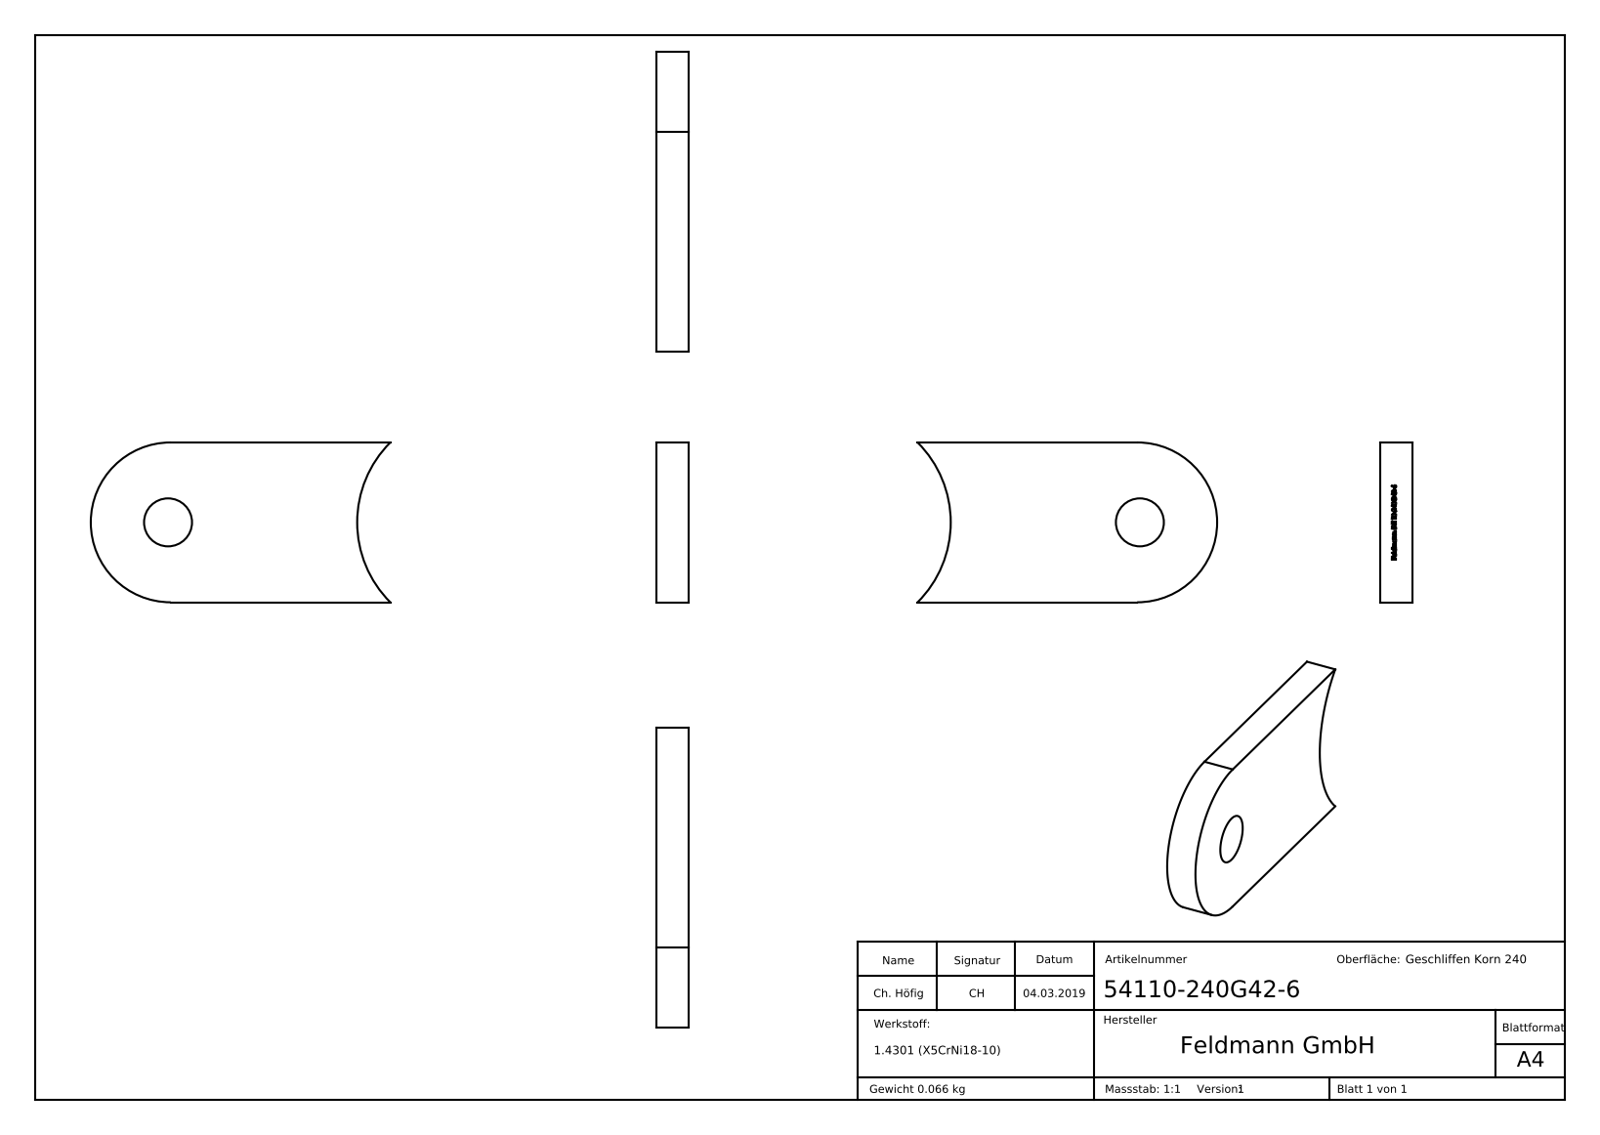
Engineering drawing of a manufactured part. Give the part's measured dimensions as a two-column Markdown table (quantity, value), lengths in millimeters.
| quantity | value |
| --- | --- |
| part name | 54110-240G42-6 |
| STEP written by | SolidWorks 2015 (CONFIG_CONTROL_DESIGN) |
| units | millimeters |
| bodies | 1 solid, 282 faces (142 planar, 36 cylindrical, 104 other) |
| overall size | 56.22 × 30 × 6 |
| volume | 8 387 mm³ |
| surface area | 3 950 mm² |
| round holes (diameter × count) | 9 × 1 |
| partial cylindrical surfaces (radius × count) | 15 × 1, 21.2 × 1, 21.3 × 1 |
| main face-to-face distances | 6, 30, 3, 2.82, 0.61, 0.53, 3.26, 2.74, 3.35, 0.71 |
